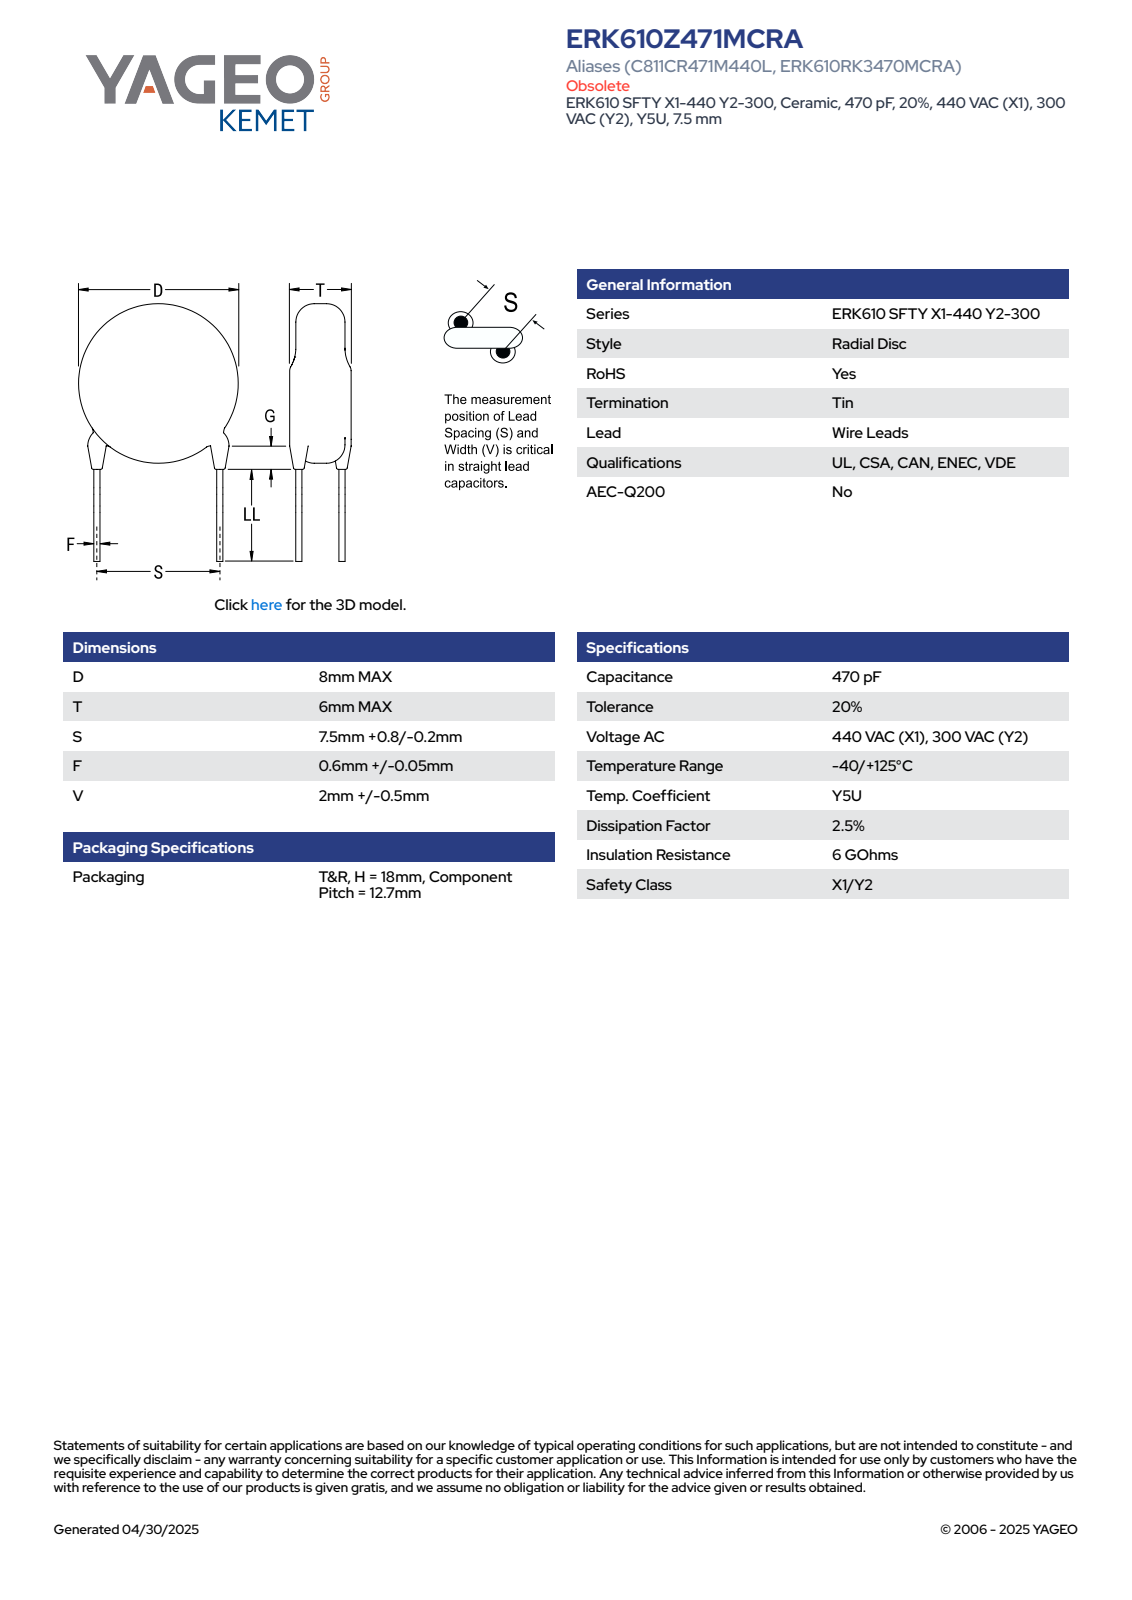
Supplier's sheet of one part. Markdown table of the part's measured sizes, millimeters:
| quantity | value |
| --- | --- |
| part name | CCD_KST_8X6_D8T6S7.5LL11F0.65G3V2.5 |
| STEP written by | SolidWorks 2014 (AUTOMOTIVE_DESIGN) |
| units | millimeters |
| bodies | 4 solids, 81 faces (63 planar, 6 cylindrical, 12 other) |
| overall size | 19.16 × 8 × 6 |
| volume | 301 mm³ |
| surface area | 287 mm² |
| round bosses / shafts (diameter × count) | 0.65 × 2, 8 × 1 |
| main face-to-face distances | 6, 1, 15.66, 14.66, 1.12, 4.07, 0.81, 0.62, 0.36, 2.95 |
